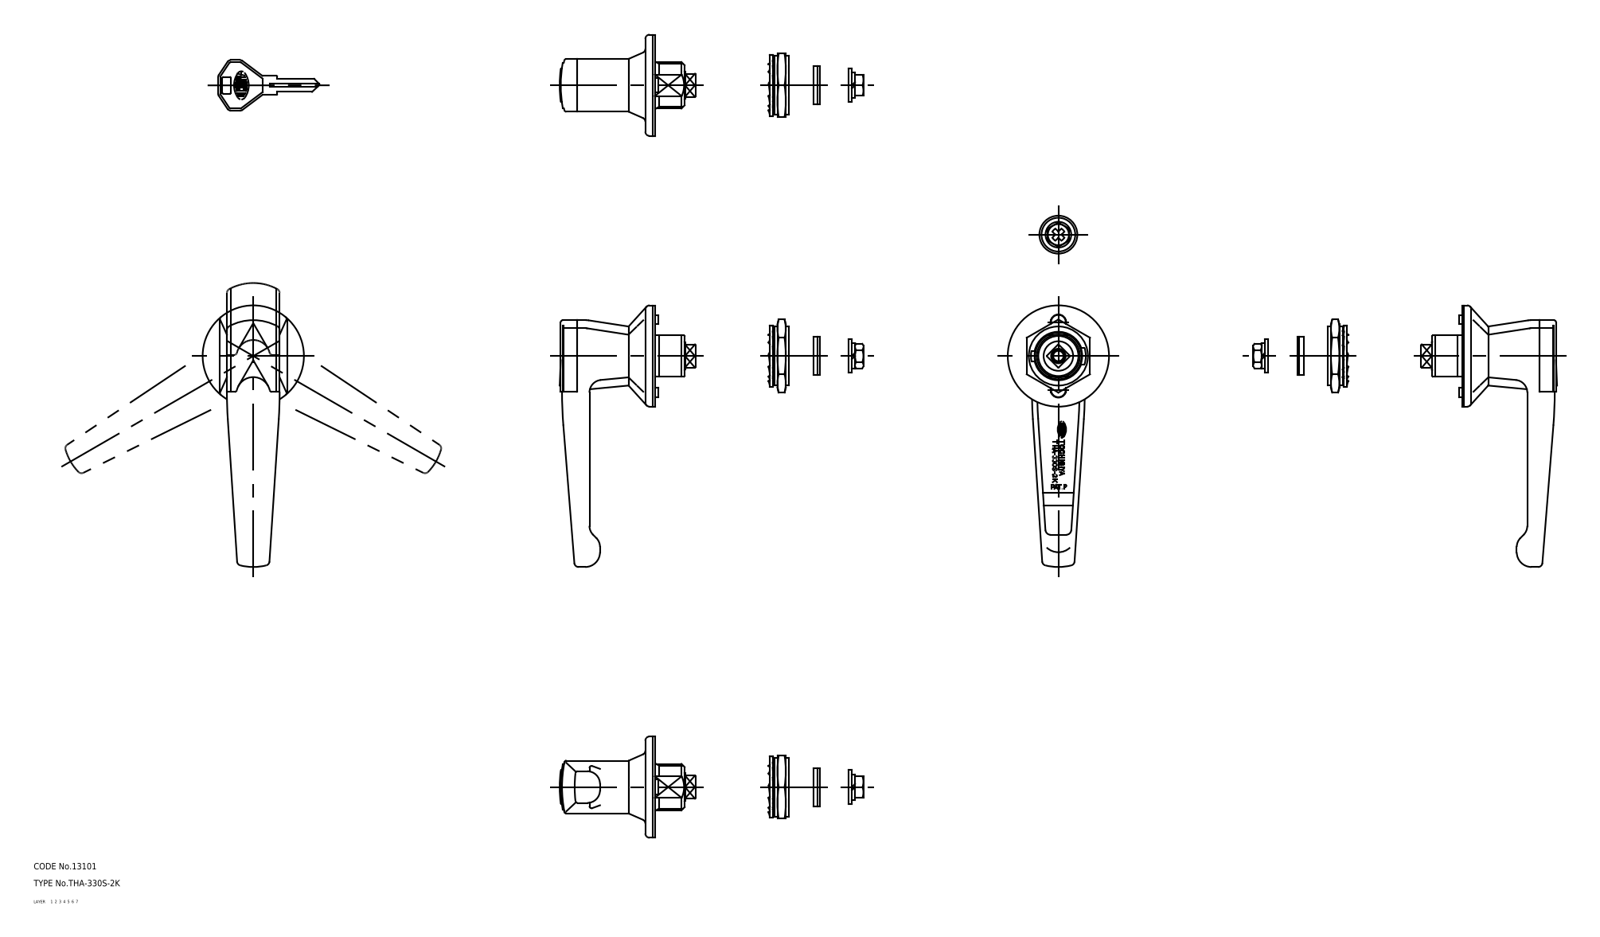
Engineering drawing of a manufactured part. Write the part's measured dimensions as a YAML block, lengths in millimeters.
part_name: "key; washer_D; washer_C; washer_B (+8 more)"
step_written_by: "CADfix (AUTOMOTIVE_DESIGN)"
units: millimeters
bodies: {solids: 11, faces: 384, planar: 0, cylindrical: 0, other: 384}
overall_size: [131.64, 124, 48]
volume: 59326
surface_area: 29884
